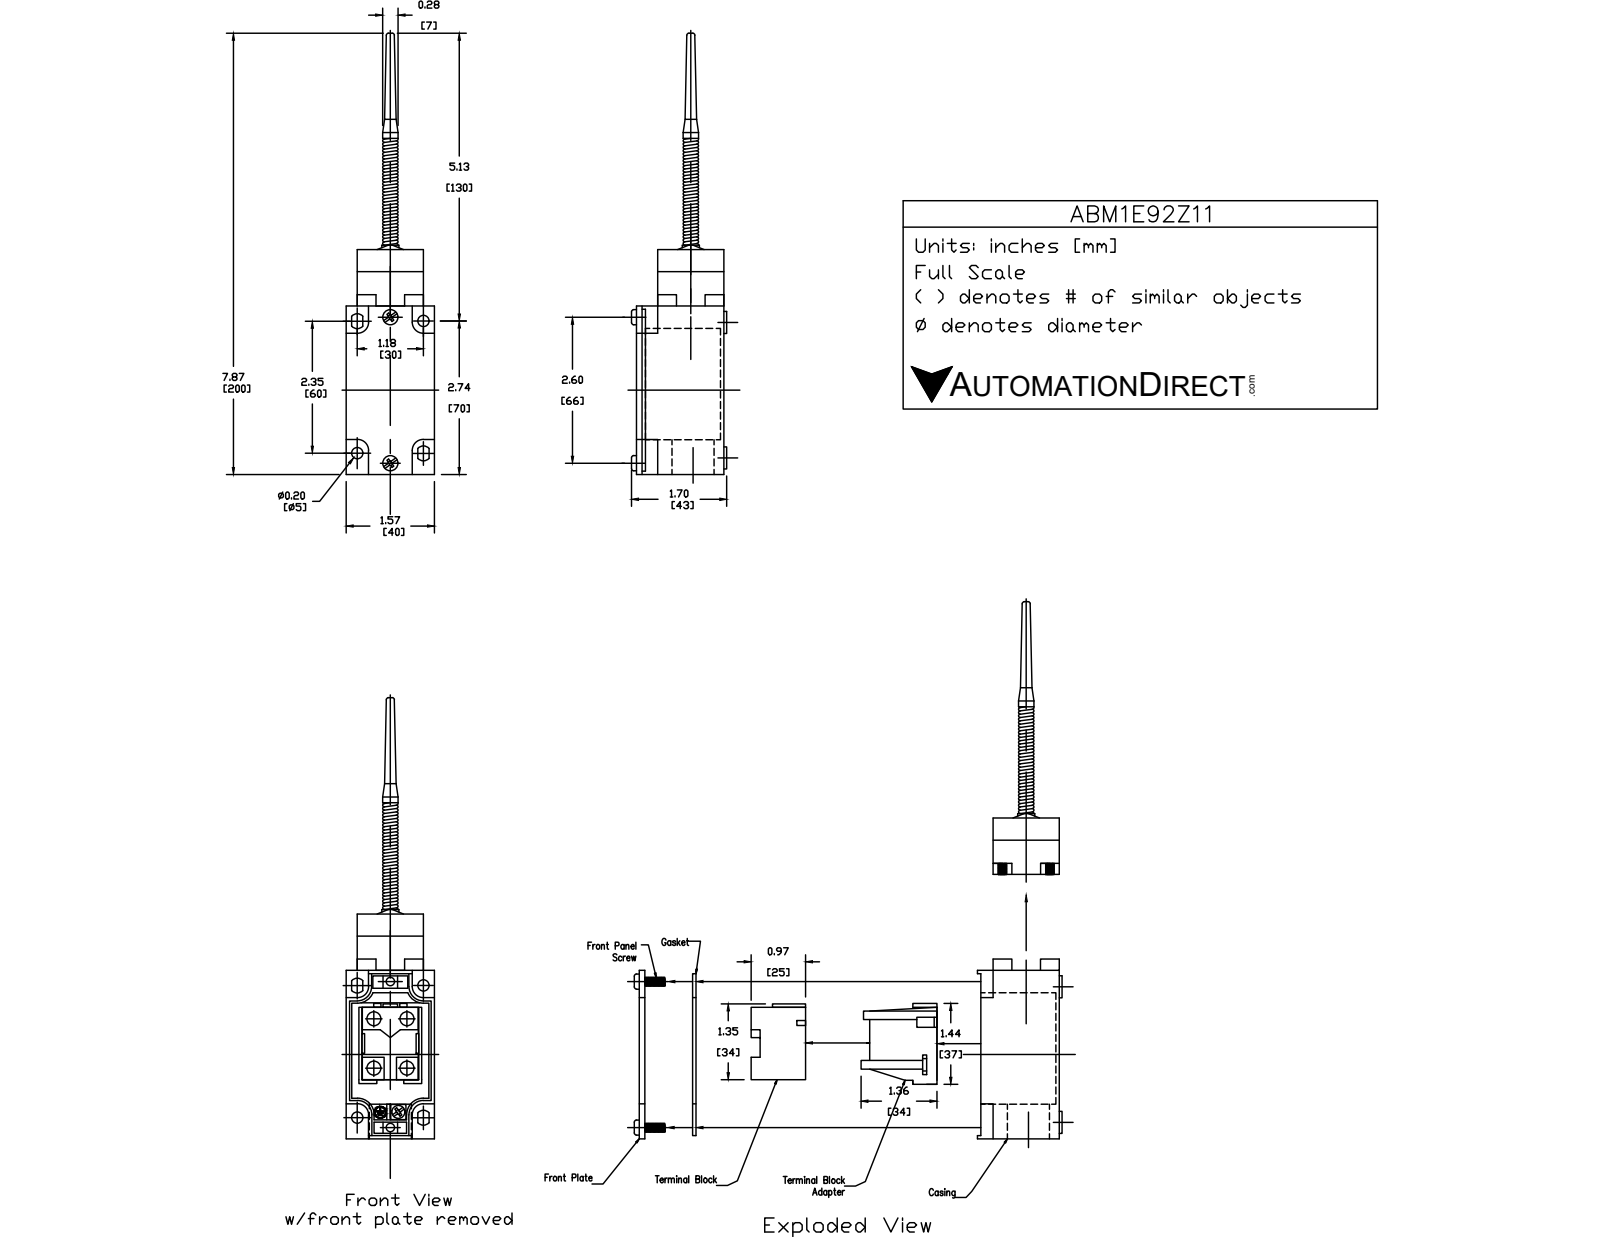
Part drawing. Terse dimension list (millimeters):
name: ABM1E92Z11
written by: SolidWorks 2017 (AUTOMOTIVE_DESIGN)
unit: mm
bodies: 3 solids, 201 faces (79 planar, 84 cylindrical, 38 other)
size: 197.8 × 43.3 × 40
volume: 129 600 mm³; area: 24 980 mm²
holes: 2× ⌀5.2, 1× ⌀17, 1× ⌀19, 1× ⌀20.5
bosses: 6× ⌀7, 4× ⌀10, 1× ⌀19, 1× ⌀11.7, 1× ⌀6.8
rounds: 16× R1.5, 4× R0.5, 4× R0.6, 4× R5, 2× R3.3, 1× R11.5, 1× R12
face distances: 40, 39.5, 30, 5, 76.5, 9.5, 35, 77, 0.5, 81.5
hole spacings: 1, 67.1
